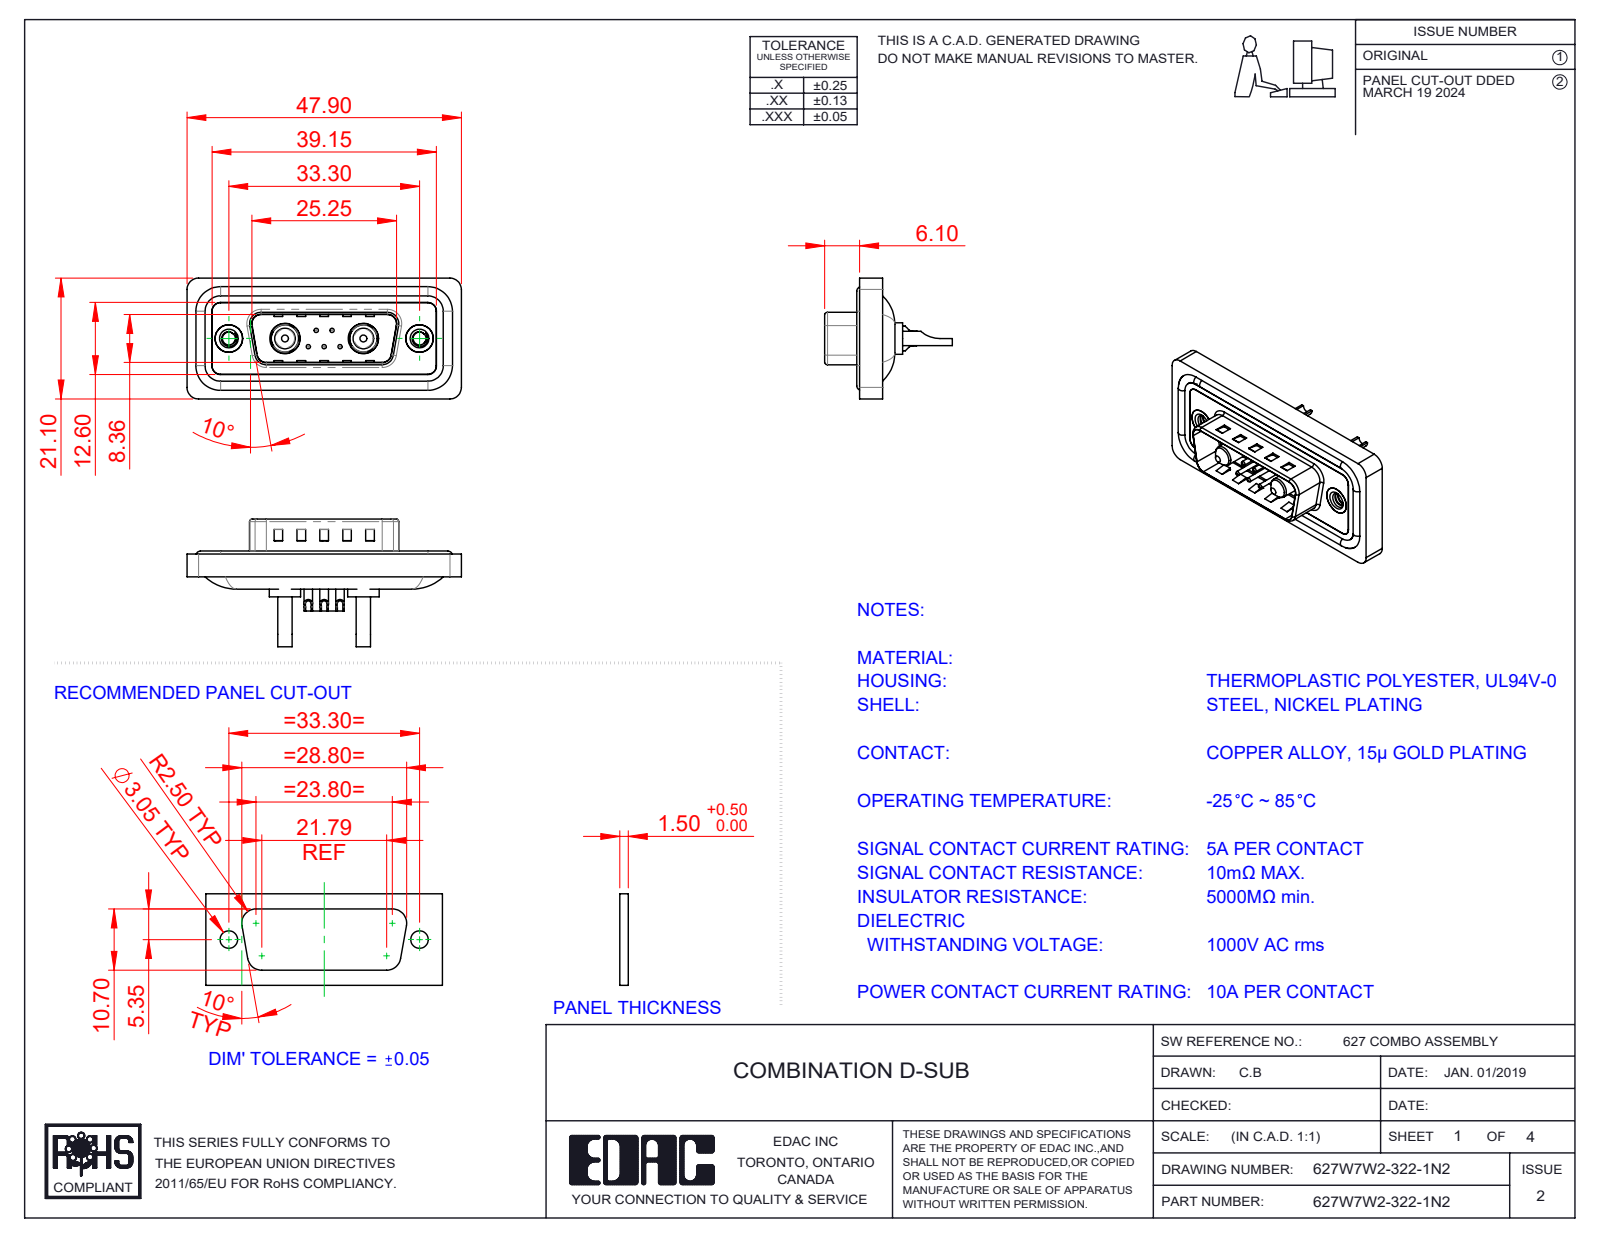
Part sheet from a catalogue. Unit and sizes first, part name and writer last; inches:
Units: inches
Overall size (bounding box): 1.886 × 0.878 × 0.831
Round holes (diameter × count): ⌀0.03 ×5, ⌀0.039 ×5, ⌀0.063 ×5, ⌀0.079 ×5, ⌀0.067 ×2, ⌀0.089 ×2, ⌀0.157 ×2, ⌀0.189 ×2, ⌀0.191 ×2, ⌀0.197 ×2, ⌀0.209 ×2
Round bosses / shafts (diameter × count): ⌀0.059 ×5, ⌀0.063 ×4, ⌀0.217 ×2, ⌀0.205 ×2, ⌀0.193 ×2, ⌀0.187 ×2, ⌀0.148 ×2, ⌀0.142 ×2
Partial cylindrical surfaces — rounded edges, fillets, slot ends (radius × count): R0.059 ×26, R0.079 ×20, R0.02 ×8, R0.063 ×8, R0.039 ×6, R0.01 ×4, R0.024 ×4, R0.026 ×4
Main face-to-face distances: 0.016, 0.043, 0.059, 0.063, 0.02, 0.122, 0.114, 0.157, 0.032, 0.377
Hole centre spacings: 0.124, 0.109, 0.386, 0.925, 0.17, 0.17, 0.198, 0.198
Volume: 0.337 in³ · Surface area: 13.84 in²
Bodies: 16 solids, 722 faces (246 planar, 308 cylindrical, 168 other)
Part name (STEP PRODUCT): 627Combo Contact Row 2_22; 627W7W2-322-1N2; 627Combo Threaded Rivet_2; 627Combo Waterproof Housing_15 Contacts (+5 more)
STEP written by: SolidWorks 2023 (CONFIG_CONTROL_DESIGN)
